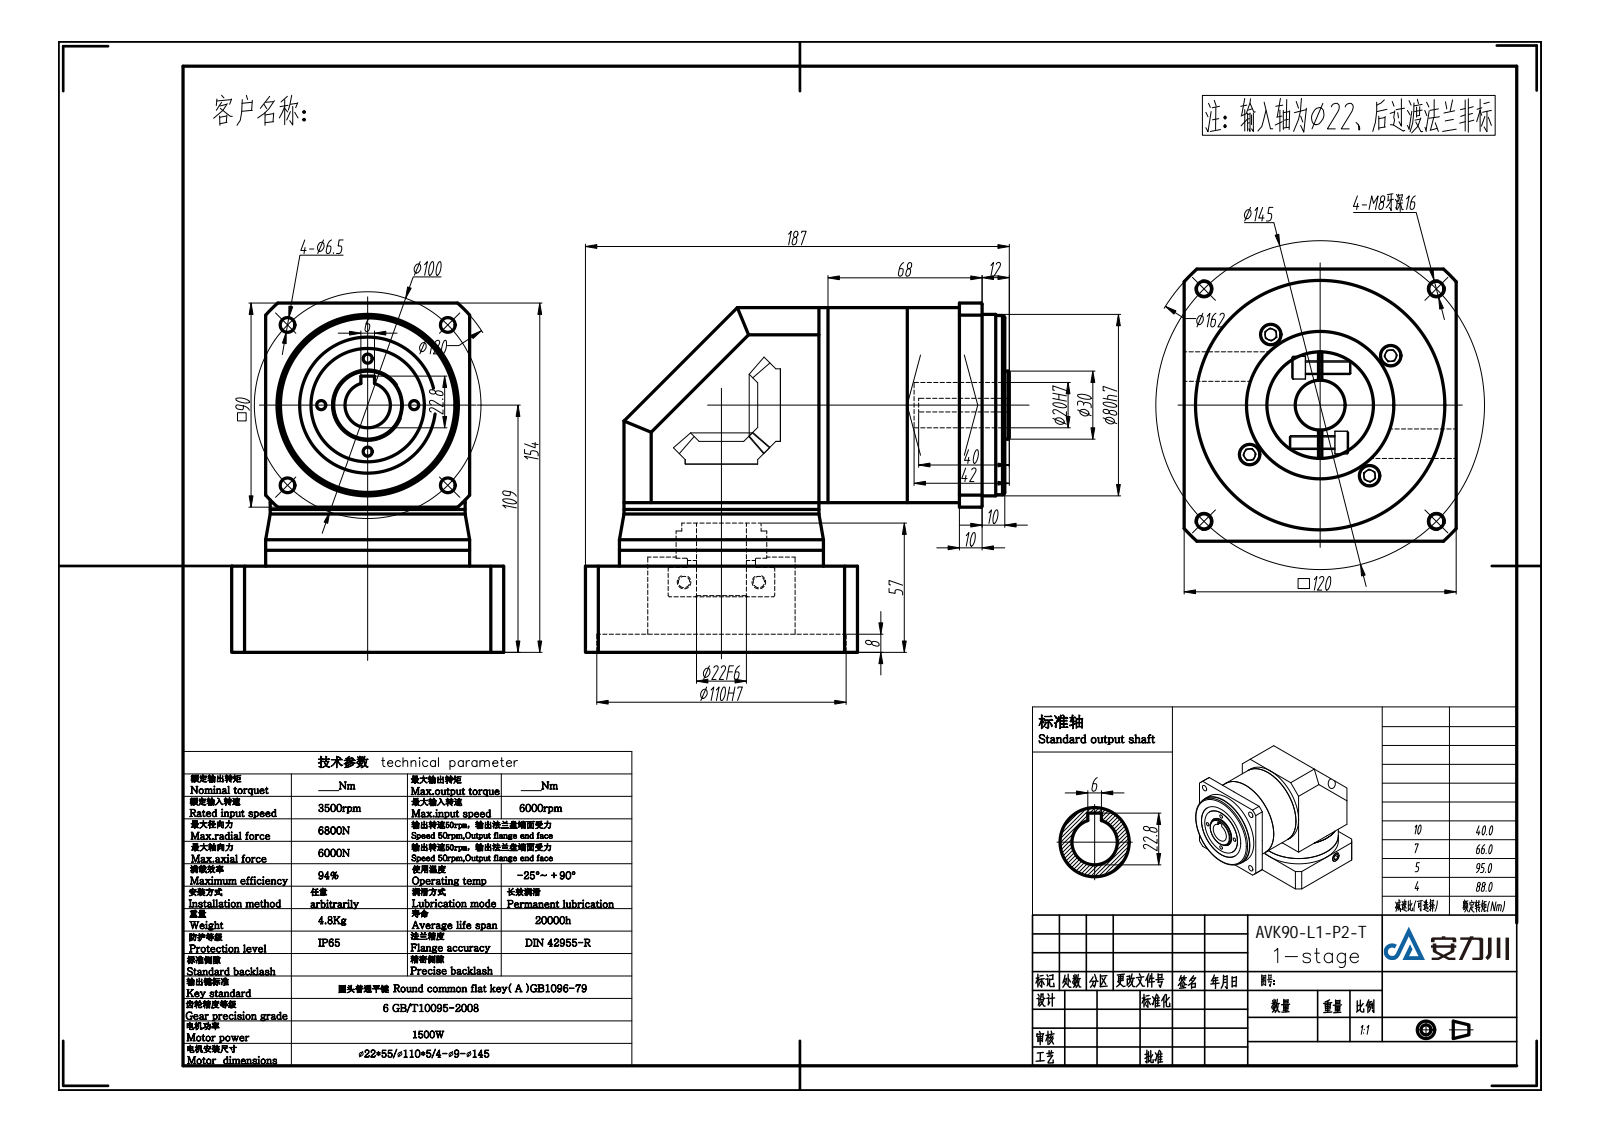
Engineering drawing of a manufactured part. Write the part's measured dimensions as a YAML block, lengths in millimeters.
part_name: "VGZK85单级模型-T（22-55 110-5 4-9-145）"
step_written_by: "SolidWorks 2016 (AUTOMOTIVE_DESIGN)"
units: millimeters
bodies: {solids: 5, faces: 325, planar: 184, cylindrical: 127, other: 14}
overall_size: [187, 154, 120]
volume: 1501000
surface_area: 188084
round_holes:
  - {diameter: 10, count: 8}
  - {diameter: 4, count: 4}
  - {diameter: 6.5, count: 4}
  - {diameter: 6.8, count: 4}
  - {diameter: 9, count: 4}
  - {diameter: 20, count: 2}
  - {diameter: 22, count: 1}
  - {diameter: 32.2, count: 1}
  - {diameter: 60, count: 1}
  - {diameter: 65, count: 1}
  - {diameter: 110, count: 1}
round_bosses_or_shafts:
  - {diameter: 8.5, count: 6}
  - {diameter: 8.4, count: 4}
  - {diameter: 86, count: 2}
  - {diameter: 30, count: 2}
  - {diameter: 9.8, count: 2}
  - {diameter: 90, count: 1}
  - {diameter: 80, count: 1}
  - {diameter: 79, count: 1}
partial_cylinders:
  - {radius: 60, count: 1}
  - {radius: 81, count: 1}
face_to_face_distances: [17, 103, 18, 35, 55, 7, 120, 25, 86, 45]
hole_center_spacings: [38, 38.36, 66.11, 20.61, 20.82, 35.61, 49.6, 49.9]
